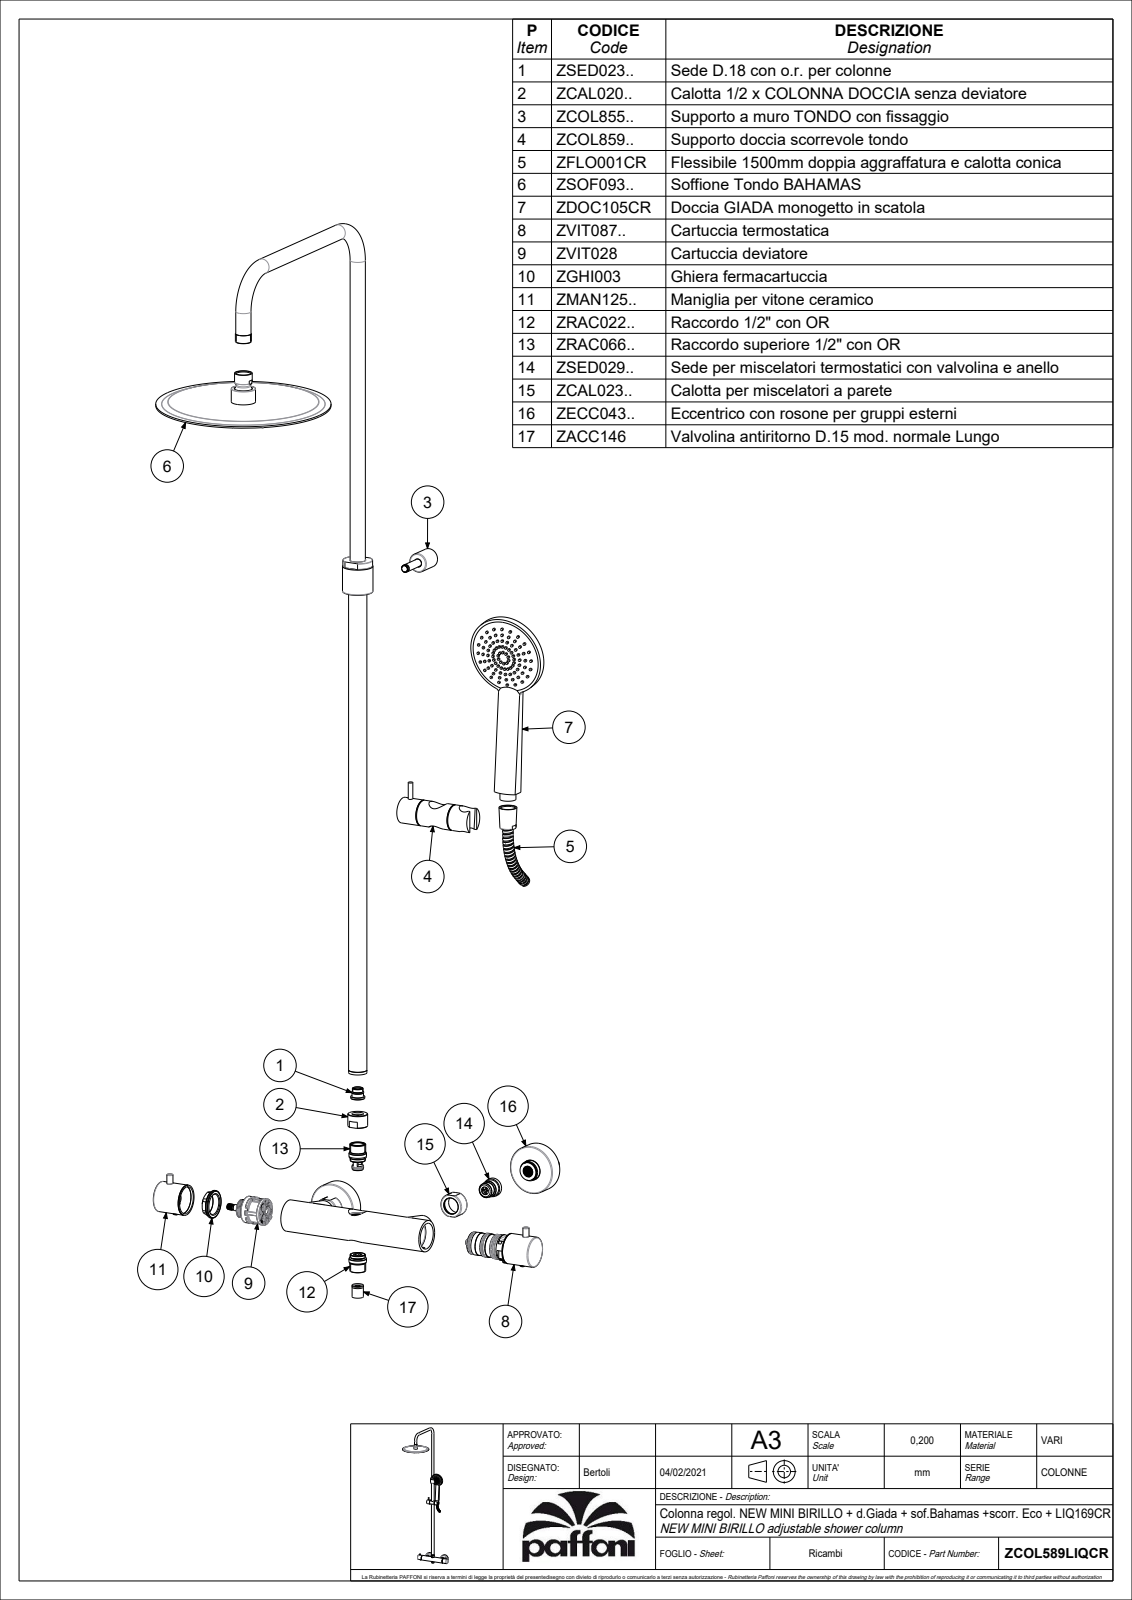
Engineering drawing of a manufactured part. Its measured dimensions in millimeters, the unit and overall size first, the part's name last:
Units: millimetres
Overall size (bounding box): 1234.1 × 497.7 × 287.73
Round holes (diameter × count): ⌀1.5 ×76, ⌀1.7 ×76, ⌀4 ×4, ⌀7 ×4, ⌀10.5 ×3, ⌀15.1 ×3, ⌀16 ×3, ⌀17 ×3, ⌀24.5 ×3, ⌀25 ×3, ⌀2.5 ×2, ⌀3 ×2
Round bosses / shafts (diameter × count): ⌀3 ×84, ⌀10 ×77, ⌀40 ×3, ⌀24 ×3, ⌀20 ×3, ⌀63.5 ×2, ⌀28 ×2, ⌀27 ×2
Partial cylindrical surfaces — rounded edges, fillets, slot ends (radius × count): R1.5 ×69, R1 ×6, R1.75 ×4, R2.75 ×2, R4 ×2, R6.5 ×2, R8.5 ×2, R15.6 ×2
Main face-to-face distances: 1, 4, 3, 5, 2, 2.4, 1.4, 1.6, 2.6, 0.4
Hole centre spacings: 32.11, 52.74, 67.32, 17.56, 34.44, 50, 61.06, 74.83
Volume: 812 461 mm³ · Surface area: 601 584 mm²
Bodies: 6 solids, 5387 faces (2103 planar, 1115 cylindrical, 2169 other)
Part name (STEP PRODUCT): ZCOL589LIQCR
STEP written by: CREO PARAMETRIC BY PTC INC, 2020044 (CONFIG_CONTROL_DESIGN)
